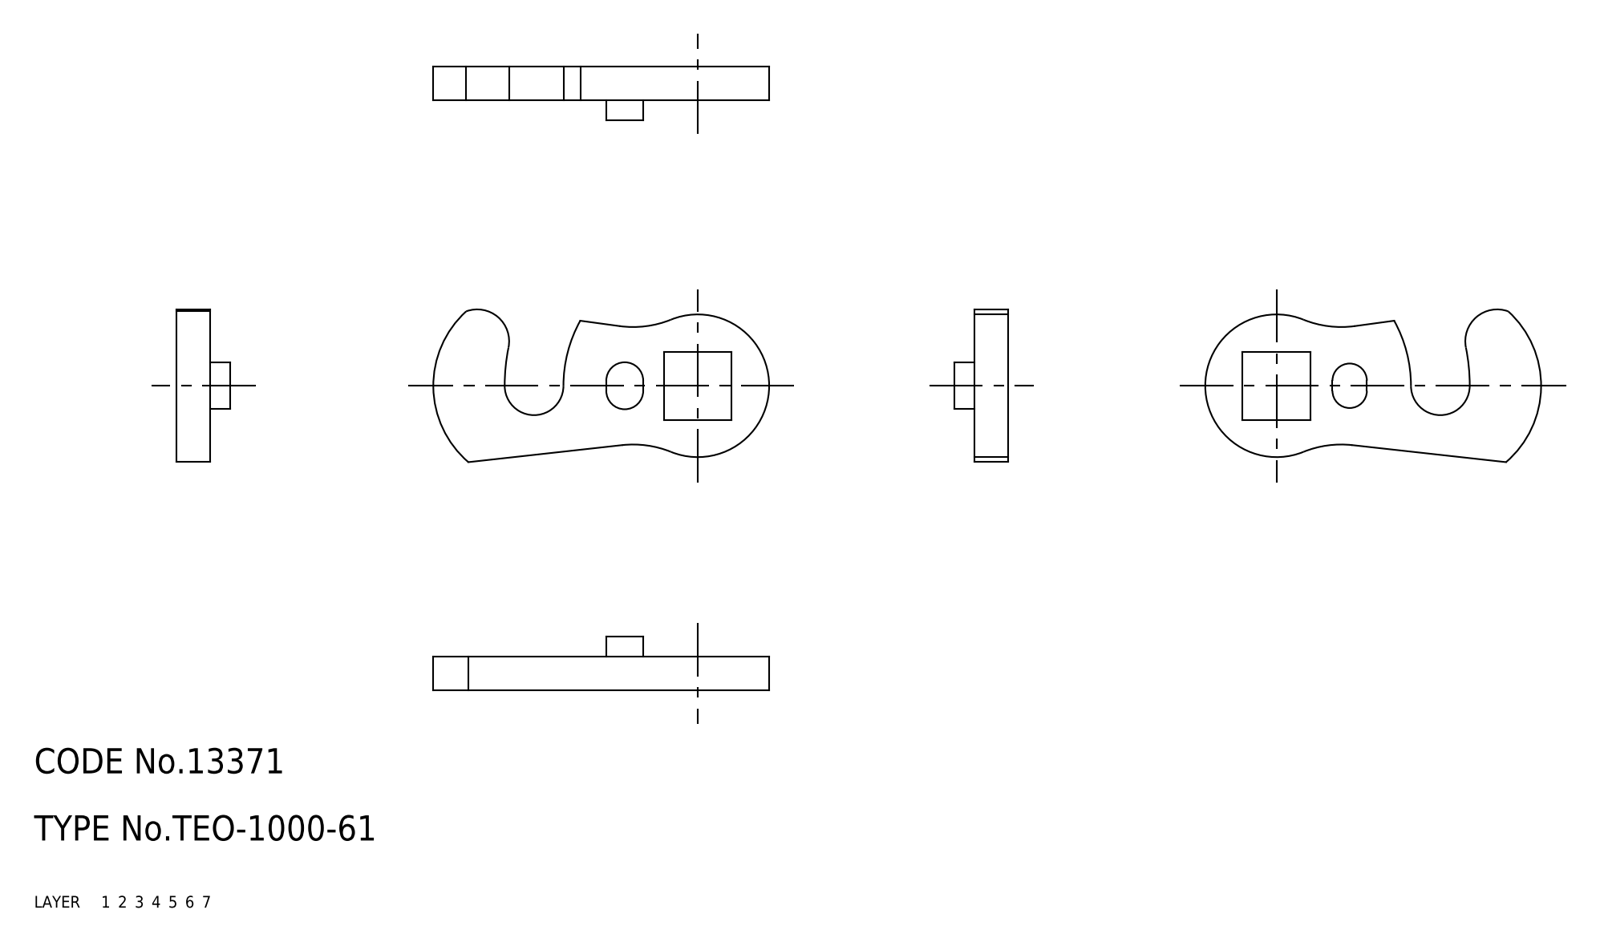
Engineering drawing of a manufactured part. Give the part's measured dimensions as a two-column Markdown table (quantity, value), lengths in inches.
| quantity | value |
| --- | --- |
| part name | cam |
| STEP written by | CADfix (AUTOMOTIVE_DESIGN) |
| units | inches |
| bodies | 1 solid, 30 faces (0 planar, 0 cylindrical, 30 other) |
| overall size | 1.575 × 0.717 × 0.252 |
| volume | 0.111 in³ |
| surface area | 2.468 in² |
